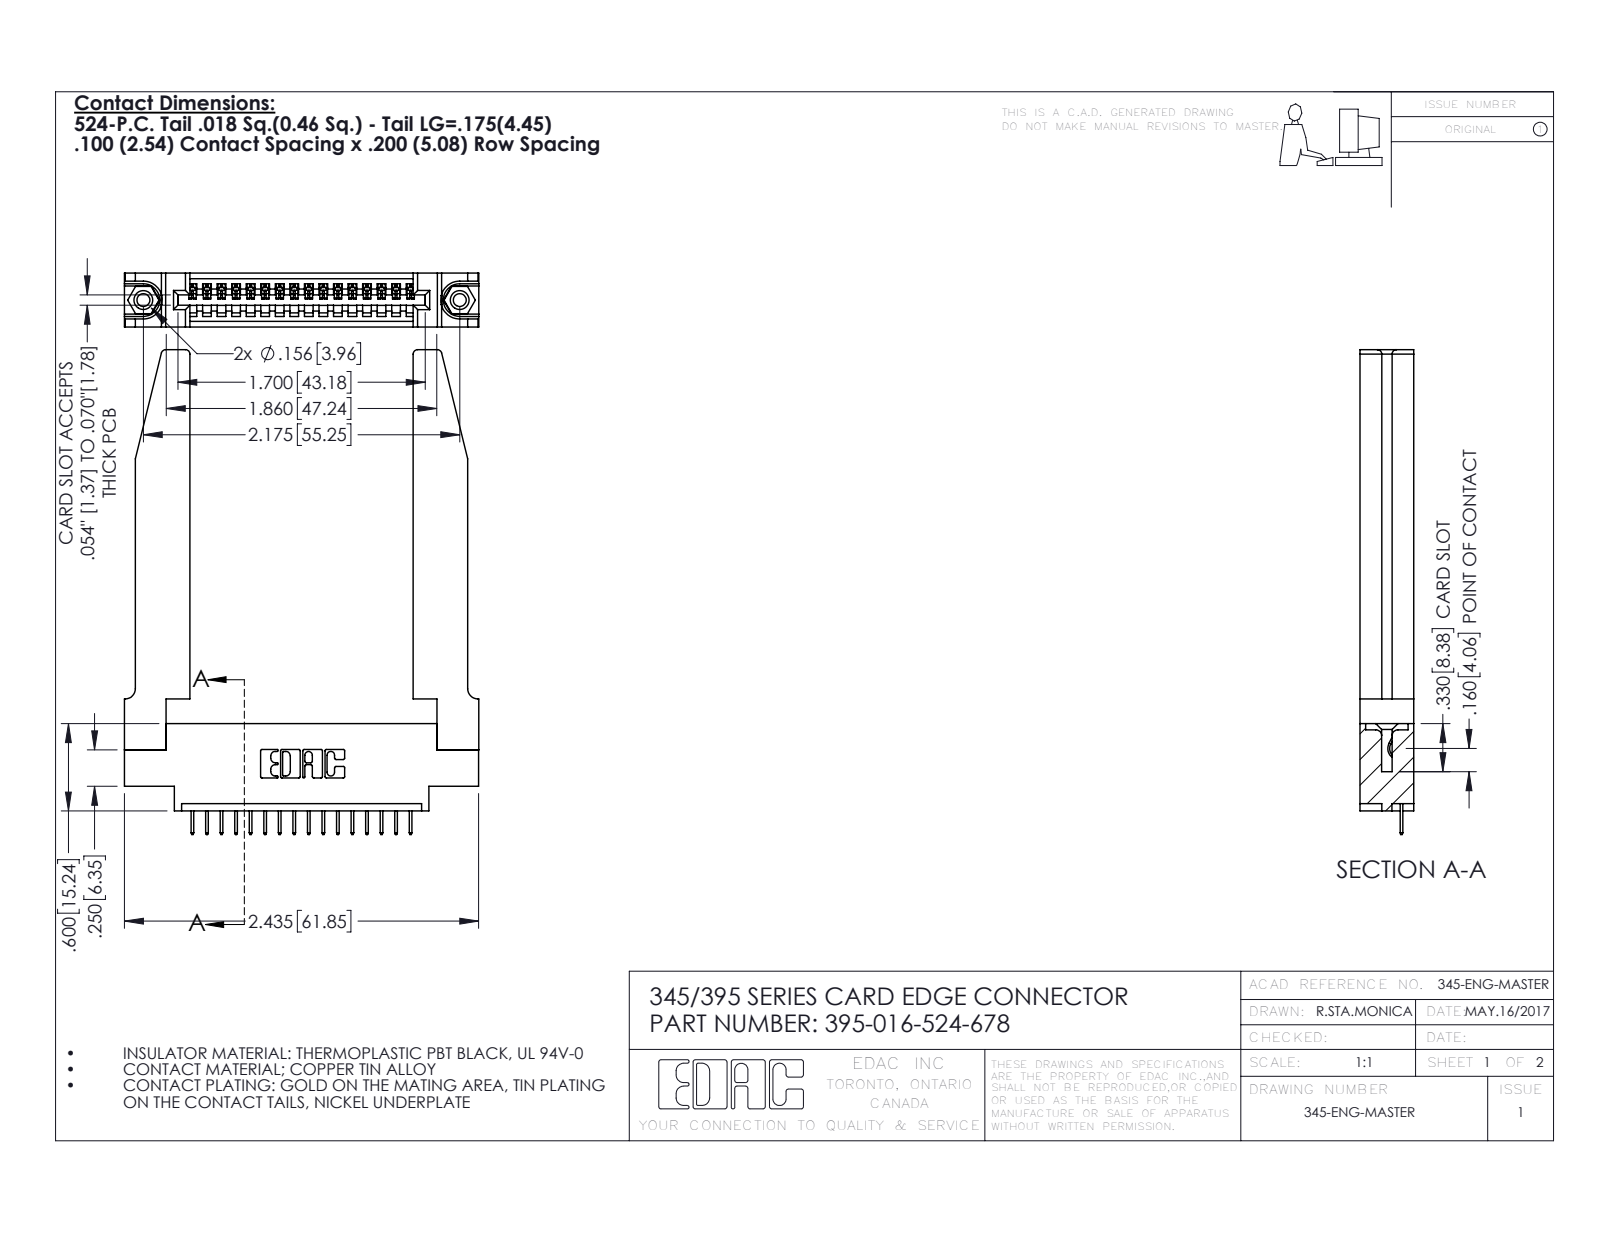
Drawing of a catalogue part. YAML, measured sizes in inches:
part_name: "345 Part_0.170 Offset - 0.156 Dia-TH; 345-220-078_345-220-078; 345-250-001_345-250-001-102; 395-016-524-678 (+1 more)"
step_written_by: "SolidWorks 2016 (CONFIG_CONTROL_DESIGN)"
units: inches
bodies: {solids: 21, faces: 1356, planar: 962, cylindrical: 342, other: 52}
overall_size: [3.332, 2.436, 0.37]
volume: 0.809
surface_area: 21.25
round_holes:
  - {diameter: 0.089, count: 2}
  - {diameter: 0.125, count: 2}
  - {diameter: 0.156, count: 2}
  - {diameter: 0.064, count: 1}
round_bosses_or_shafts:
  - {diameter: 0.155, count: 2}
partial_cylinders:
  - {radius: 0.006, count: 32}
  - {radius: 0.01, count: 22}
  - {radius: 0.03, count: 8}
  - {radius: 0.007, count: 6}
  - {radius: 0.031, count: 6}
  - {radius: 0.026, count: 3}
  - {radius: 0.031, count: 2}
  - {radius: 0.04, count: 2}
face_to_face_distances: [0.37, 0.072, 0.298, 0.148, 0.15, 0.22, 0.077, 1.535, 0.123, 0.098]
hole_center_spacings: [0.27, 1.942, 2.175]
